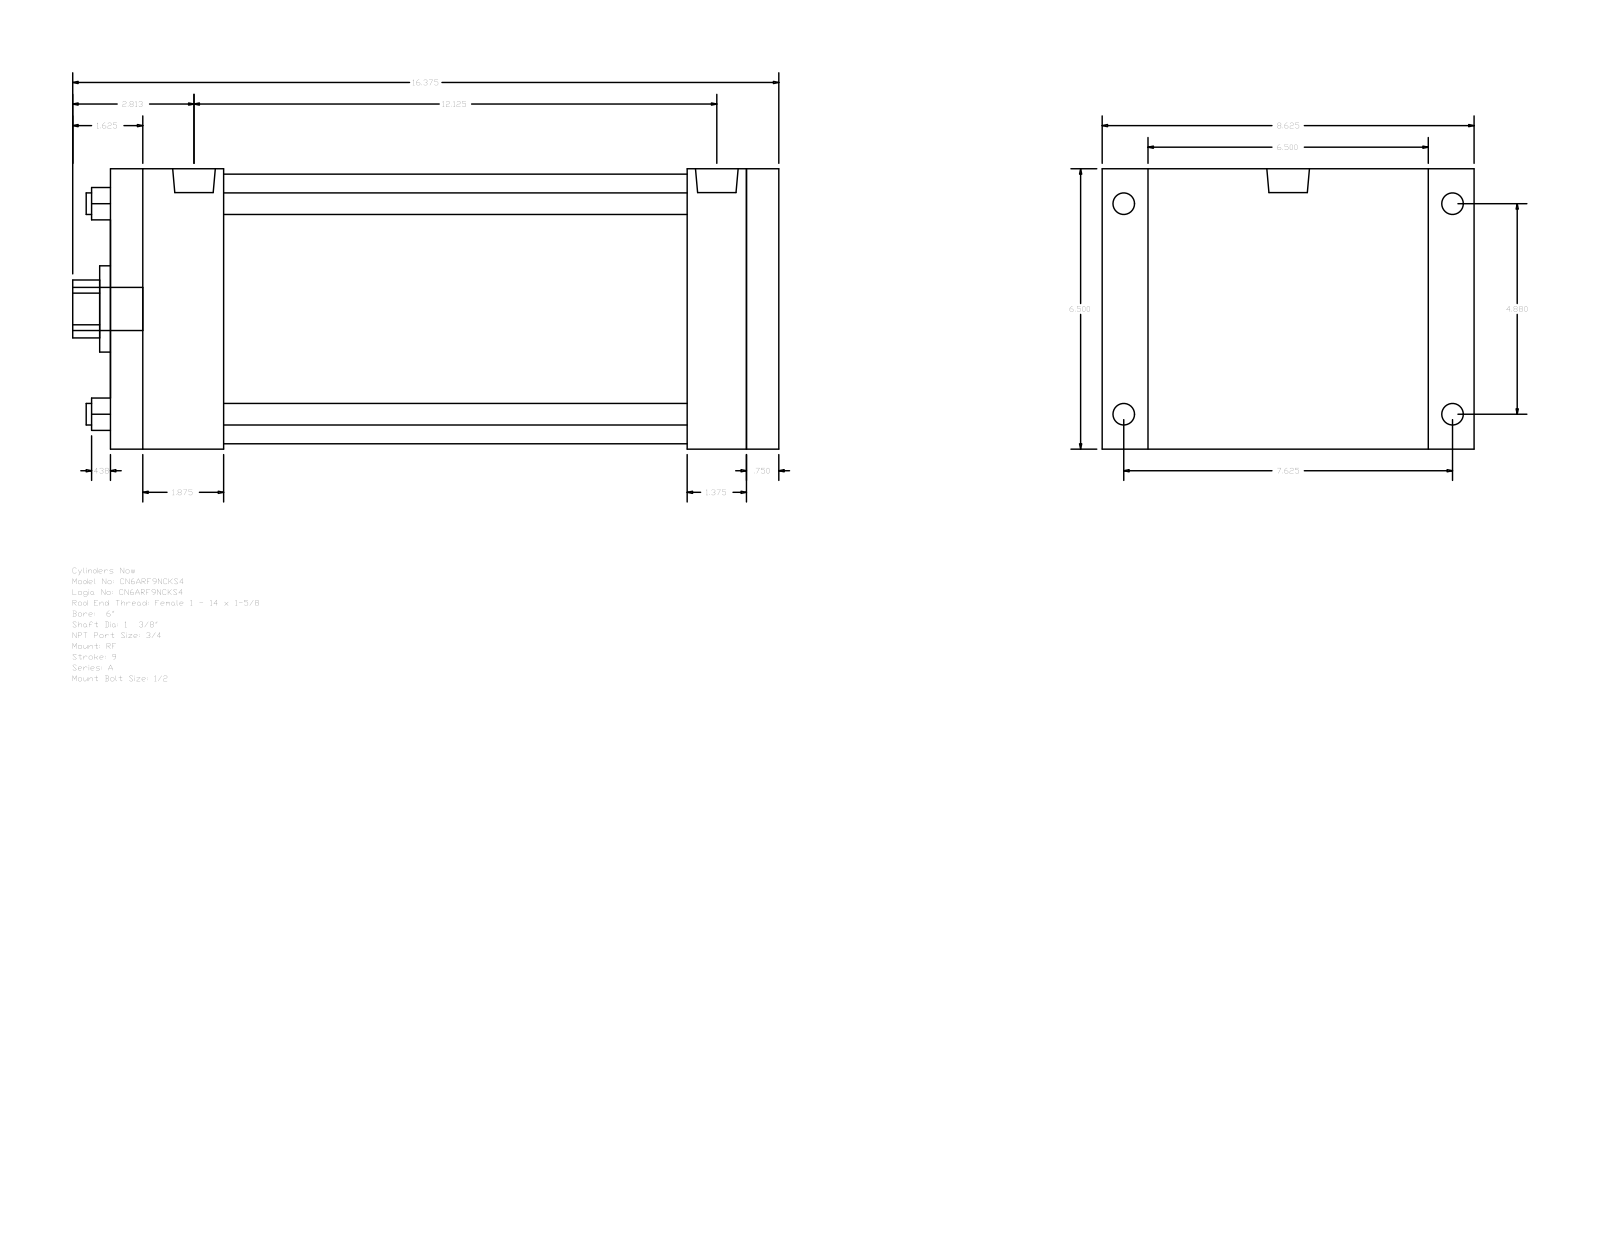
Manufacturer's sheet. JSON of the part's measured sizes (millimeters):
{"part_name": "A_RF__0600_1.375", "step_written_by": "GSSL Pune (CONFIG_CONTROL_DESIGN)", "units": "millimeters", "bodies": {"solids": 0, "faces": 92, "planar": 64, "cylindrical": 28, "other": 0}, "overall_size": [415.93, 219.07, 165.1], "round_holes": [[12.7, 4], [34.92, 1], [50.8, 1], [158.75, 1]], "round_bosses_or_shafts": [[15.08, 4], [12.7, 4], [25.12, 2], [25.4, 1]], "partial_cylinders_radius": [[17.06, 1]], "face_to_face_distances": [165.1, 393.7, 19.05, 374.65, 66.67, 307.98, 327.03, 339.72, 273.05, 34.93], "hole_center_spacings": [87.65, 123.96, 175.31]}
